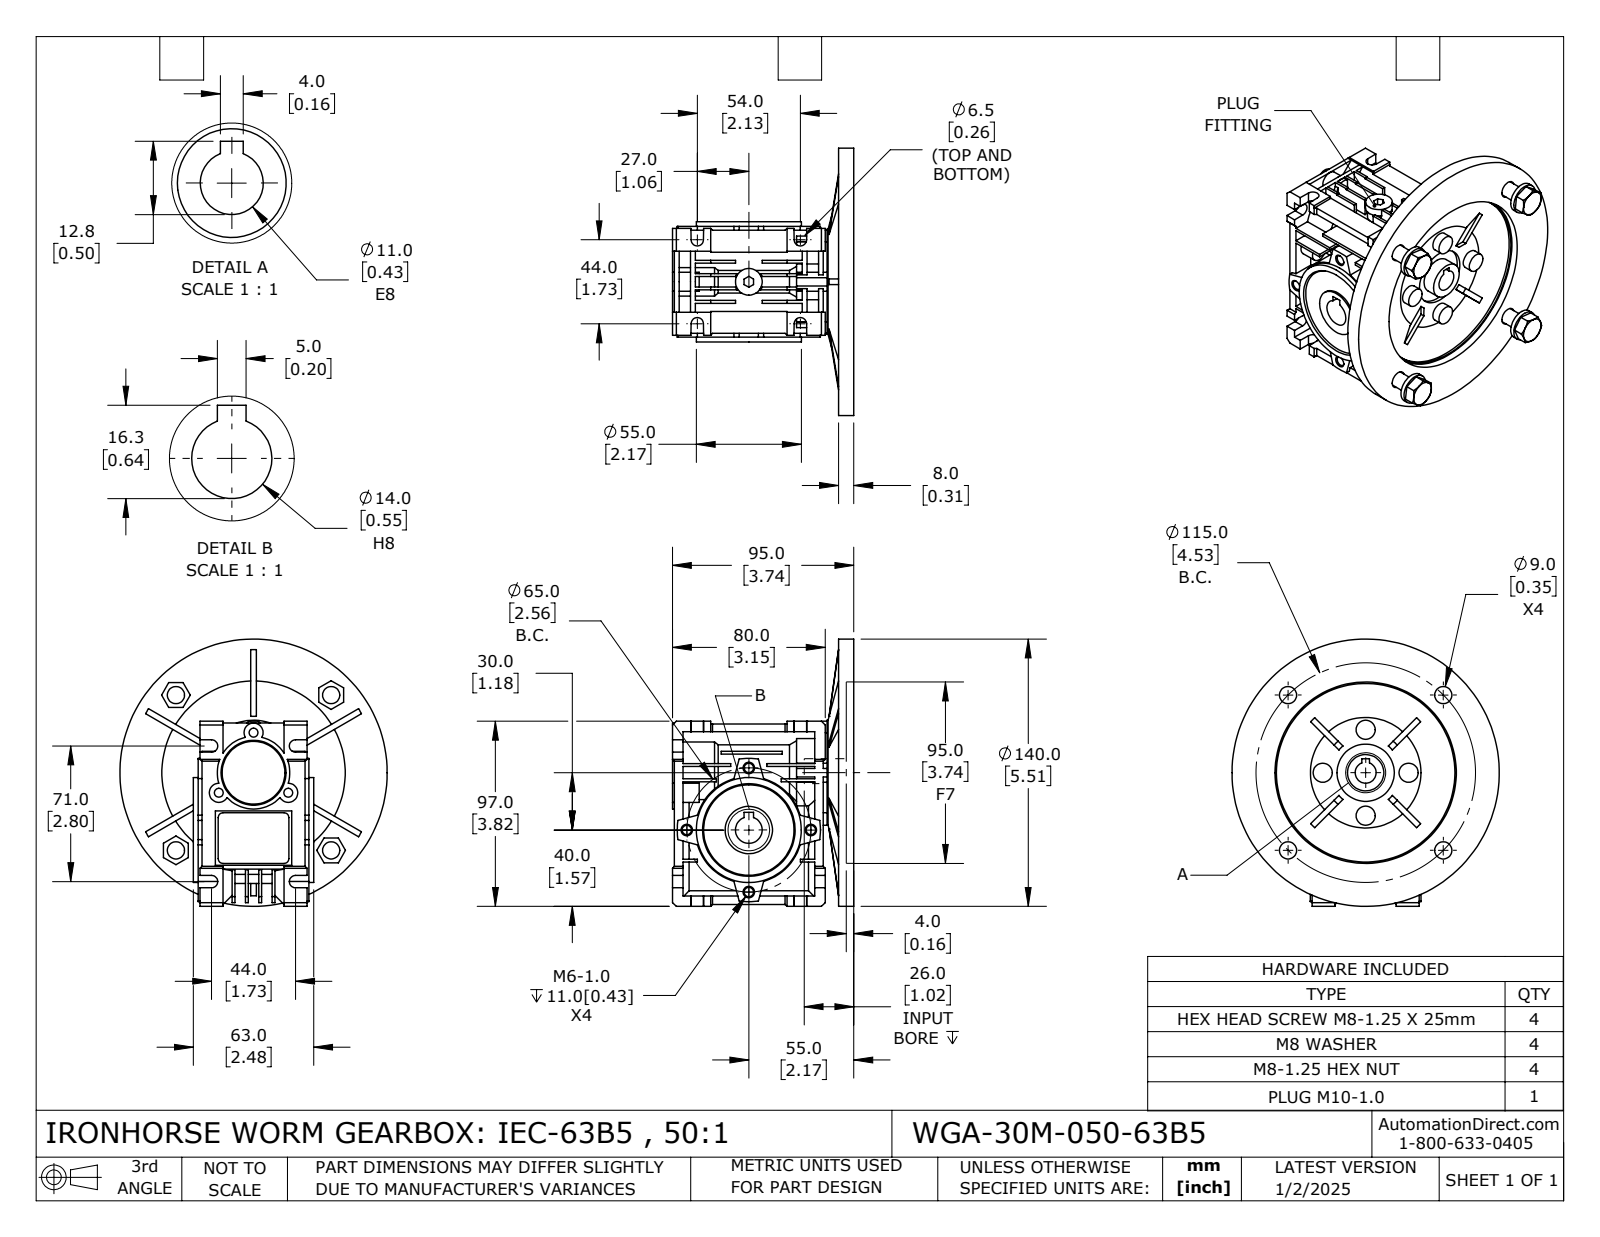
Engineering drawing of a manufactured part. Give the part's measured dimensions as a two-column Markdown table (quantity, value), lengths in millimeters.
| quantity | value |
| --- | --- |
| part name | WGA-30M-050-63B5 |
| STEP written by | SolidWorks 2024 (CONFIG_CONTROL_DESIGN) |
| units | millimeters |
| bodies | 6 solids, 836 faces (542 planar, 216 cylindrical, 78 other) |
| overall size | 140 × 140 × 95 |
| volume | 391 916 mm³ |
| surface area | 131 275 mm² |
| round holes (diameter × count) | 9 × 5, 4.92 × 4, 4.65 × 3, 4.92 × 2, 11 × 1, 11.5 × 1, 14 × 1, 14.5 × 1, 19 × 1, 24.8 × 1, 30 × 1, 93.5 × 1 |
| round bosses / shafts (diameter × count) | 10 × 4, 55 × 2, 140 × 1, 56 × 1, 38 × 1, 37 × 1, 14 × 1, 12 × 1 |
| partial cylindrical surfaces (radius × count) | 3.25 × 8, 2.5 × 4, 5 × 3, 7.5 × 1, 17 × 1, 21.5 × 1, 37.5 × 1 |
| main face-to-face distances | 8, 1.5, 7, 5.5, 1, 14, 4.5, 2, 8.5, 4 |
| hole center spacings | 32.5, 45.96, 57.5, 81.32, 21, 36.37, 37.61, 45.16 |
